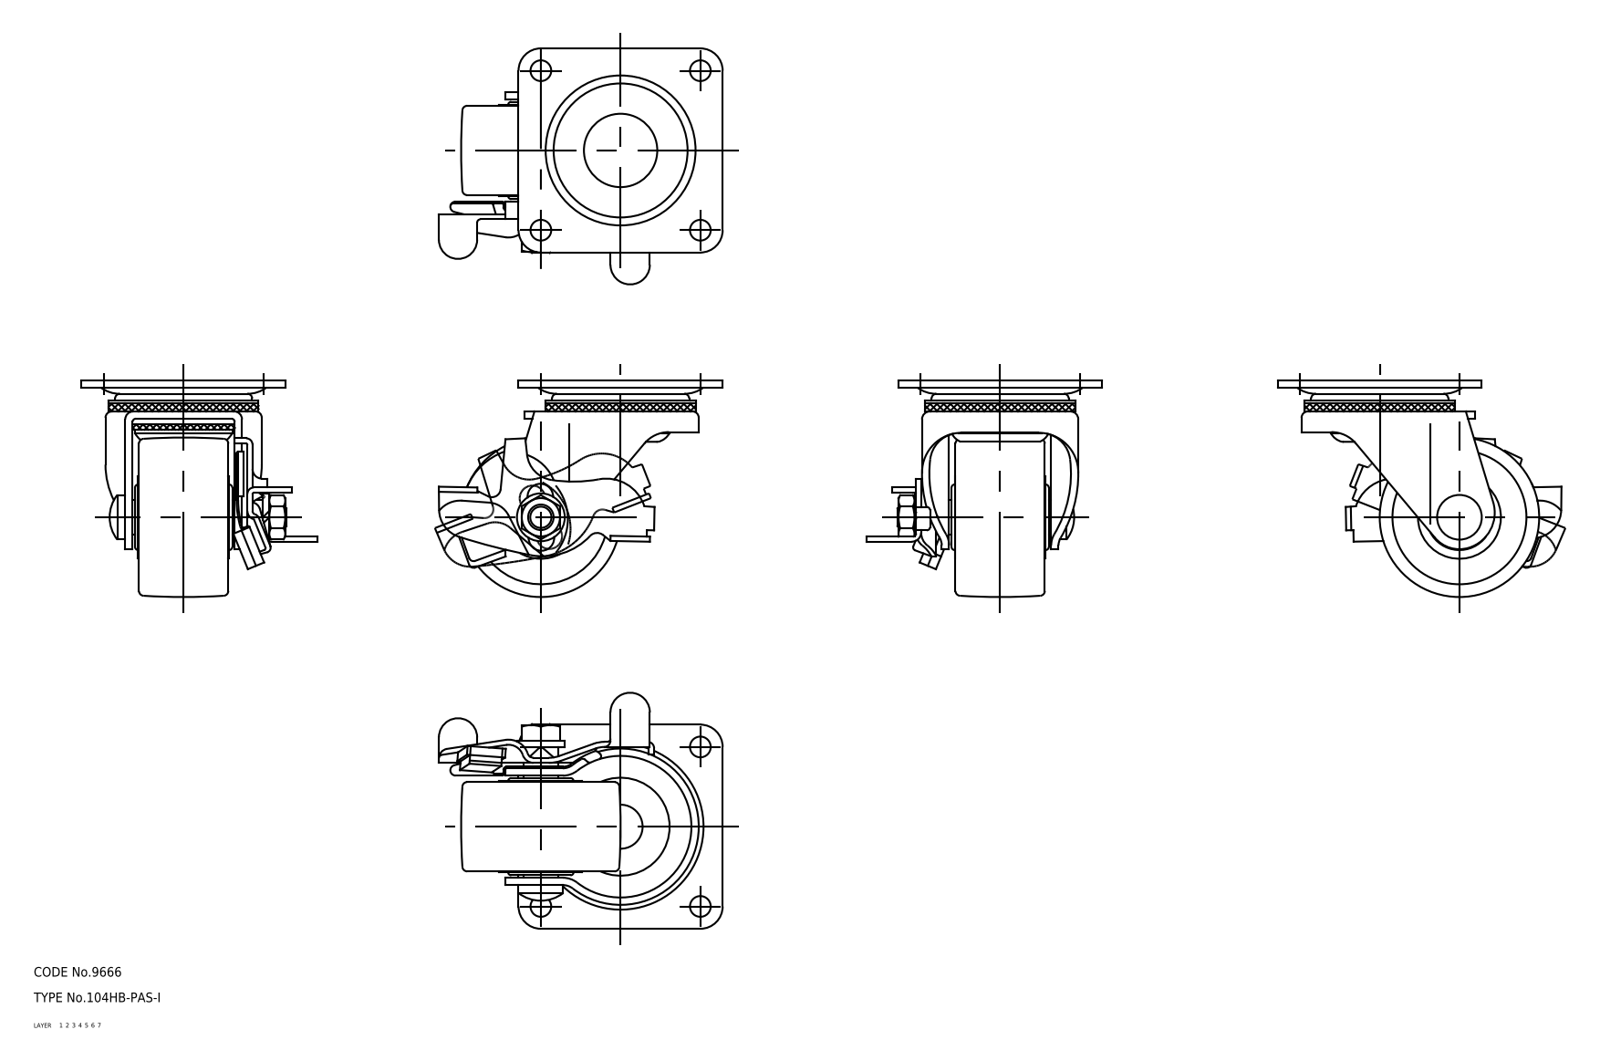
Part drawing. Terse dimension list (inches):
name: 67129106; 67129119; 67129132; 67129145 (+3 more)
written by: CADfix (AUTOMOTIVE_DESIGN)
unit: in
bodies: 7 solids, 347 faces (0 planar, 0 cylindrical, 347 other)
size: 3.504 × 2.913 × 2.677
volume: 6.056 in³; area: 61.75 in²
